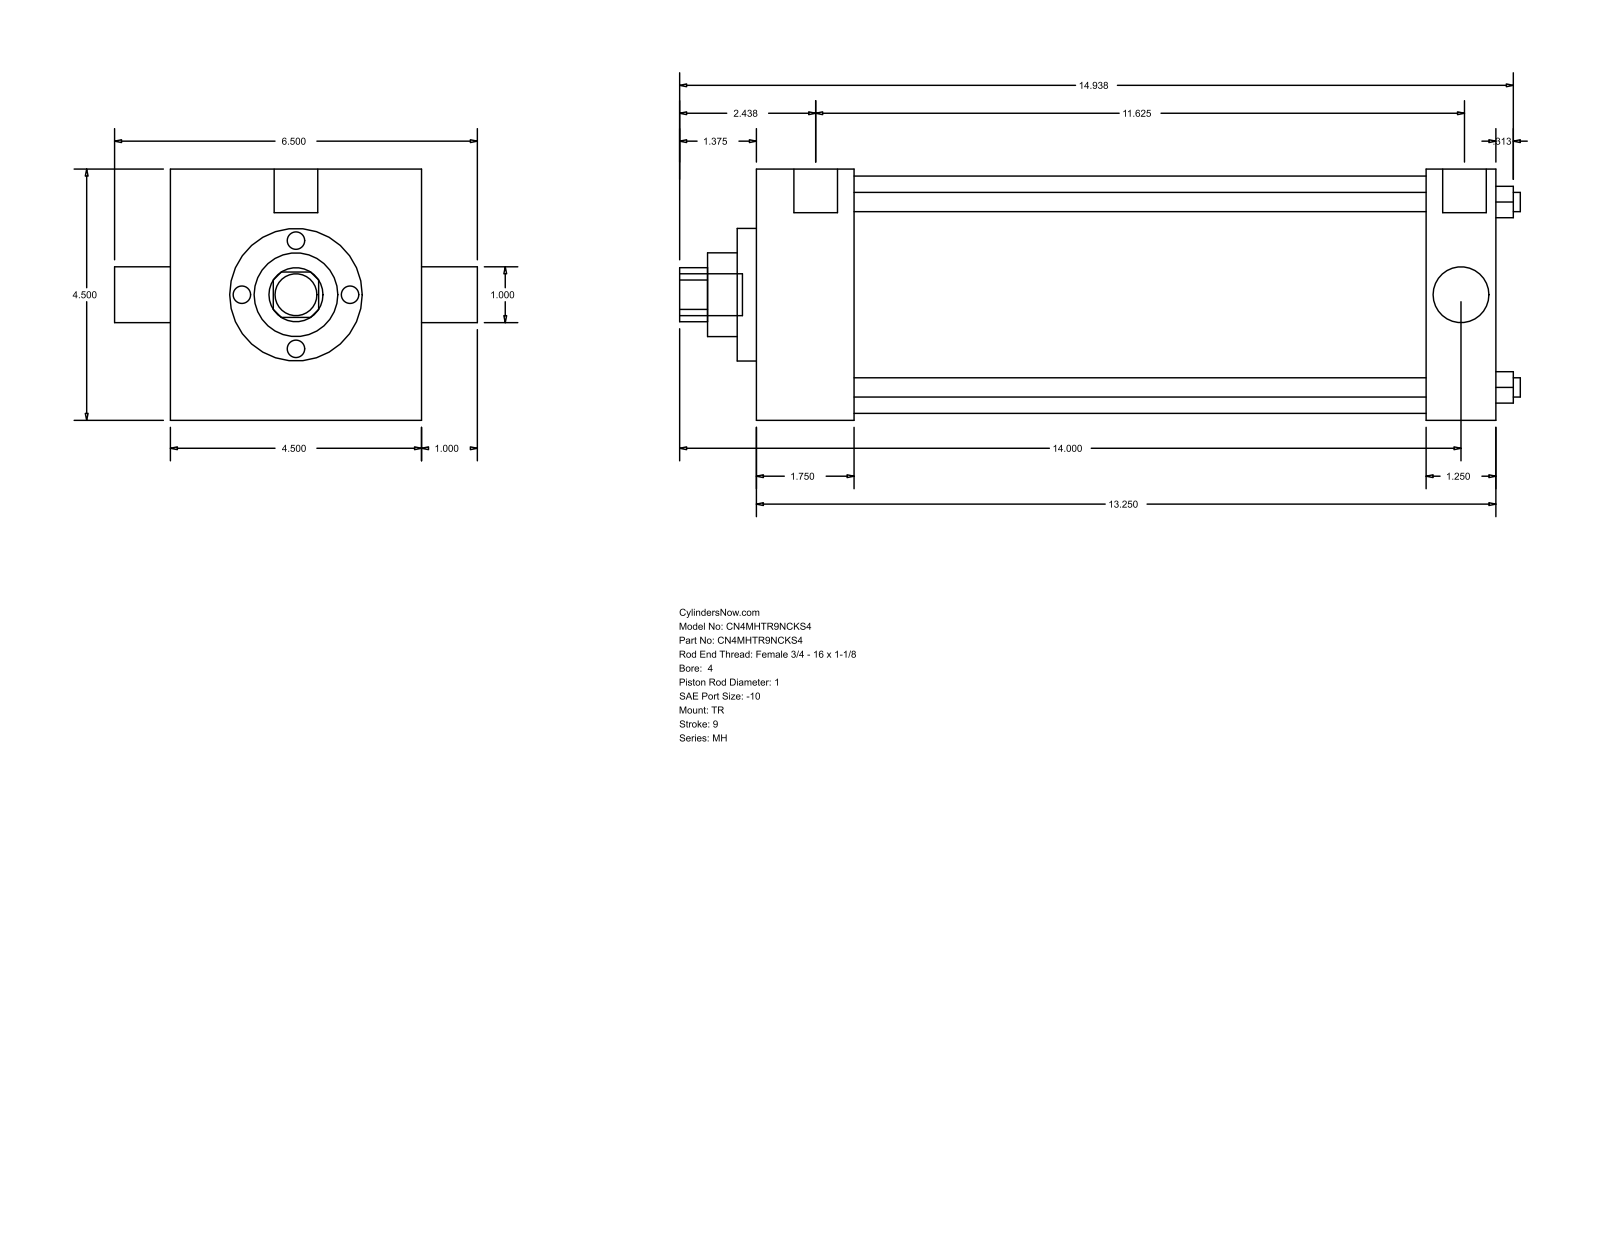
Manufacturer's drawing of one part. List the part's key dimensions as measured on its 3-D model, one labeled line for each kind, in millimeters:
Part name (STEP PRODUCT): MH_TR__0400_1
STEP written by: GSSL Pune (CONFIG_CONTROL_DESIGN)
Units: millimetres
Bodies: 0 solids, 86 faces (61 planar, 25 cylindrical, 0 other)
Overall size (bounding box): 382.59 × 165.1 × 114.3
Round holes (diameter × count): ⌀8.76 ×4, ⌀25.4 ×2, ⌀38.1 ×1, ⌀60.33 ×1, ⌀107.95 ×1
Round bosses / shafts (diameter × count): ⌀8.73 ×3, ⌀19.84 ×2, ⌀19.05 ×1
Partial cylindrical surfaces — rounded edges, fillets, slot ends (radius × count): R12.29 ×1
Main face-to-face distances: 114.3, 336.56, 44.46, 292.1, 304.81, 260.35, 31.75, 8.73, 53.19, 313.54
Hole centre spacings: 59.62, 84.32, 119.25
